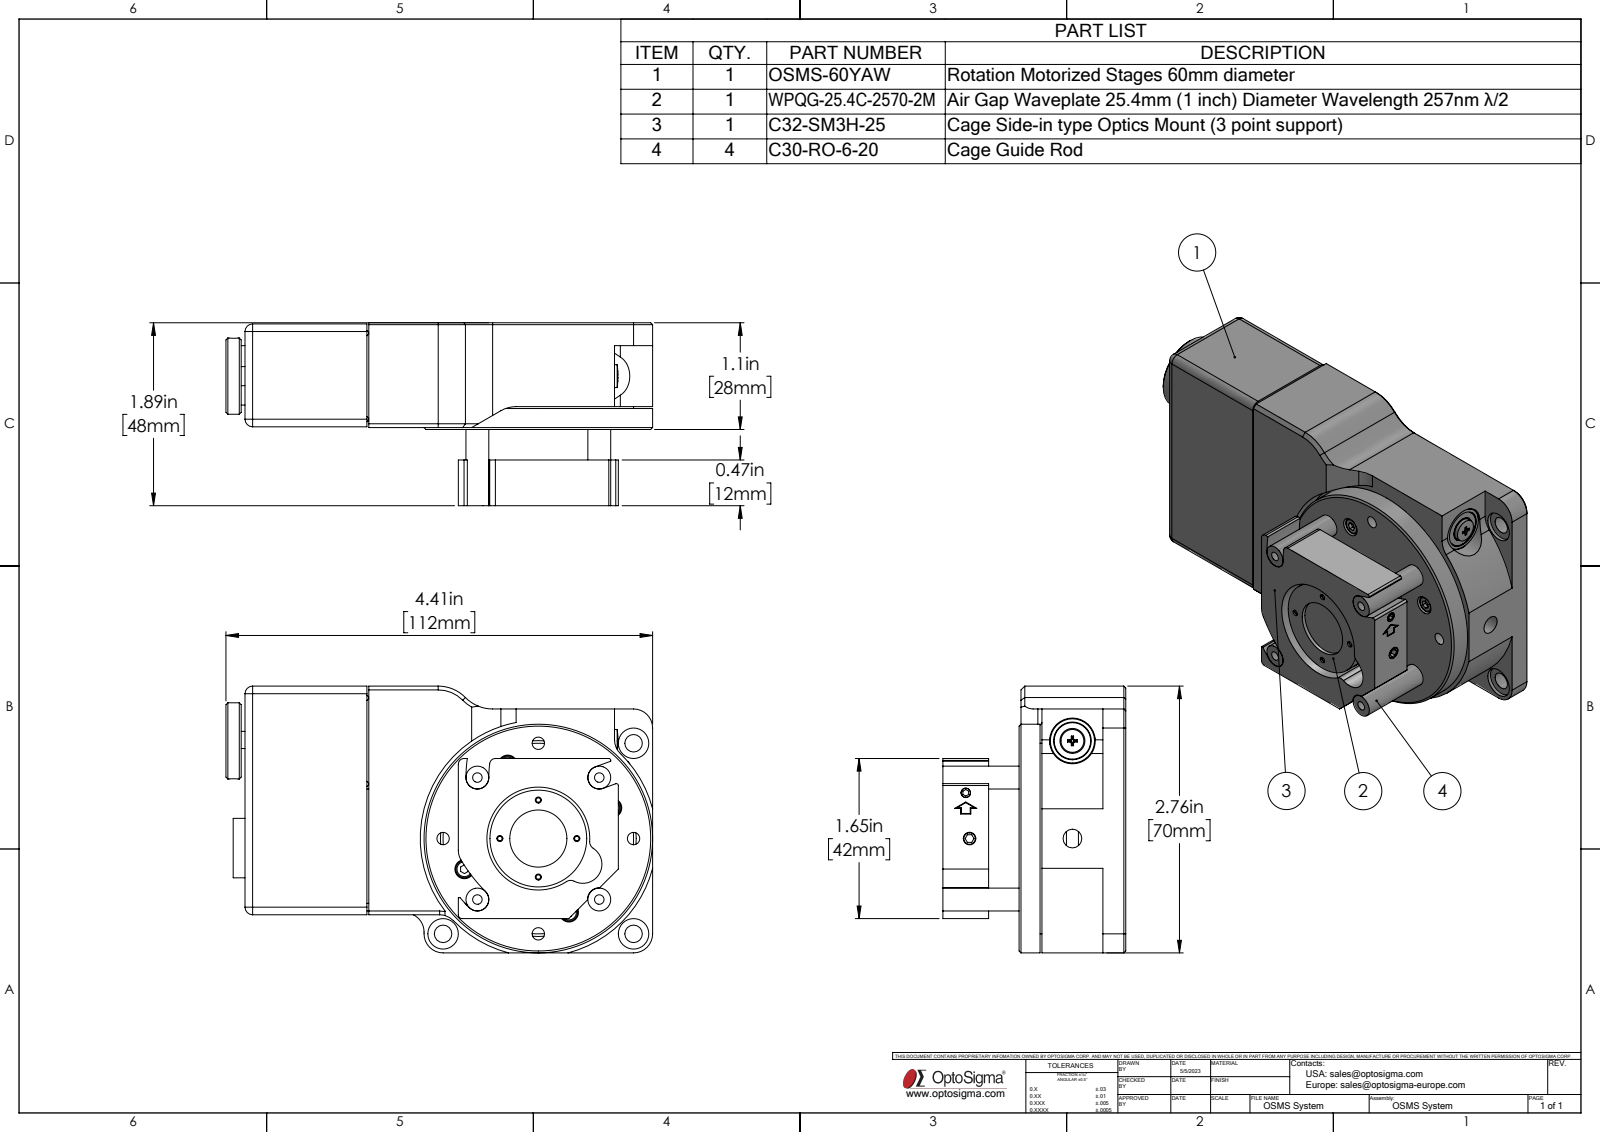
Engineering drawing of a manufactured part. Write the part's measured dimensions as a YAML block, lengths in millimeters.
part_name: "OSMS-60YAW; C30-RO-6-20; SP606YAW-M01-05001-S01^OSMS-60YAW; WPQG-25.4C-2570-2M (+2 more)"
step_written_by: "SolidWorks 2022 (AUTOMOTIVE_DESIGN)"
units: millimeters
bodies: {solids: 40, faces: 1661, planar: 940, cylindrical: 454, other: 267}
overall_size: [112, 70, 48]
volume: 139500
surface_area: 84060
round_holes:
  - {diameter: 2.6, count: 12}
  - {diameter: 1.6, count: 8}
  - {diameter: 2.5, count: 6}
  - {diameter: 3, count: 5}
  - {diameter: 5, count: 5}
  - {diameter: 1.2, count: 4}
  - {diameter: 1.8, count: 4}
  - {diameter: 2, count: 4}
  - {diameter: 2.1, count: 4}
  - {diameter: 2.4, count: 4}
  - {diameter: 2.8, count: 4}
  - {diameter: 3.3, count: 4}
round_bosses_or_shafts:
  - {diameter: 4.5, count: 15}
  - {diameter: 2.8, count: 10}
  - {diameter: 3, count: 6}
  - {diameter: 4.7, count: 4}
  - {diameter: 2.6, count: 4}
  - {diameter: 2.1, count: 4}
  - {diameter: 1.4, count: 4}
  - {diameter: 3.8, count: 3}
partial_cylinders:
  - {radius: 0.5, count: 38}
  - {radius: 2, count: 12}
  - {radius: 1, count: 11}
  - {radius: 1.5, count: 9}
  - {radius: 5, count: 8}
  - {radius: 0.2, count: 4}
  - {radius: 0.2, count: 4}
  - {radius: 0.3, count: 4}
face_to_face_distances: [1, 26, 2, 0.5, 5, 6, 25, 21.7, 20.7, 5.5]
hole_center_spacings: [28.6, 17.9, 39.4, 42, 21, 30, 5.1, 8.3]
